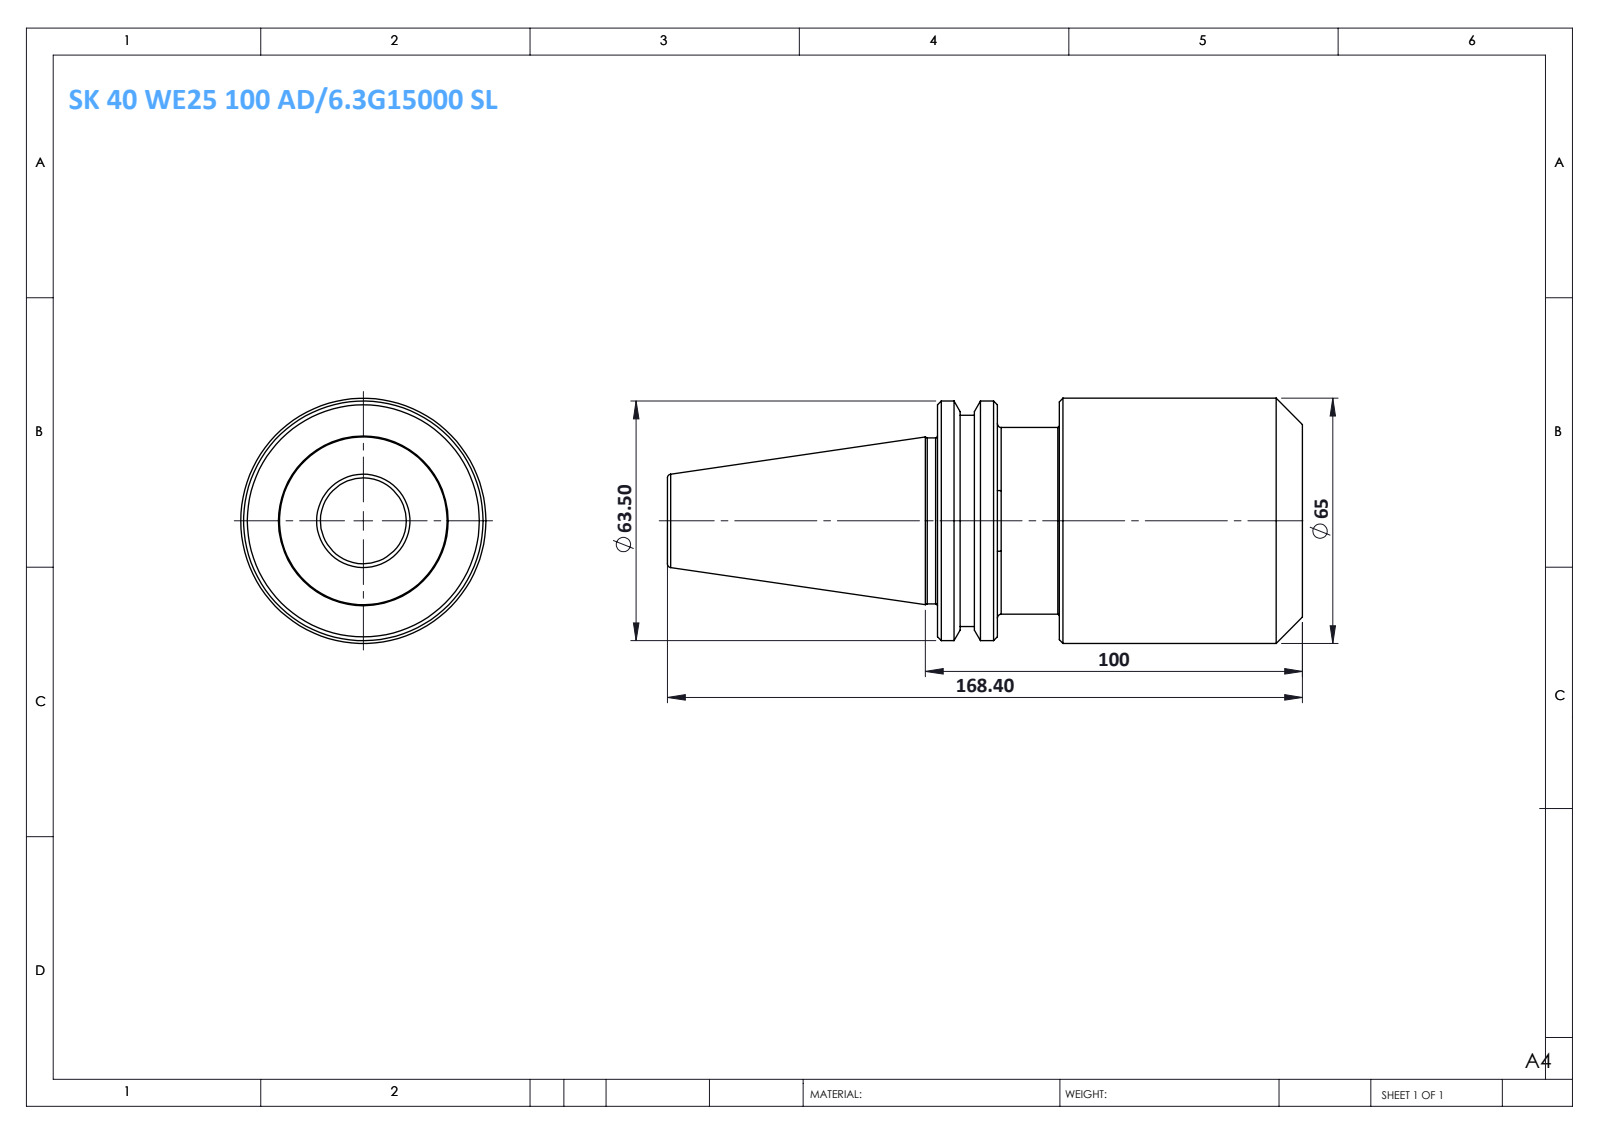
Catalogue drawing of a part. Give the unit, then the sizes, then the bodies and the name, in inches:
Units: inches
Overall size (bounding box): 6.63 × 2.559 × 2.559
Round bosses / shafts (diameter × count): ⌀2.559 ×1, ⌀2.5 ×1, ⌀2.205 ×1, ⌀1.949 ×1, ⌀1.732 ×1
Main face-to-face distances: 3.811, 2.539, 1.272, 3.185, 0.646, 0.626, 6.63, 4.091, 3.445, 2.819
Volume: 21.85 in³ · Surface area: 53.23 in²
Bodies: 1 solid, 44 faces (8 planar, 12 cylindrical, 24 other)
Part name (STEP PRODUCT): SK40 WE25 100 AD-6.3G15000 SL
STEP written by: SolidWorks 2014 (CONFIG_CONTROL_DESIGN)
